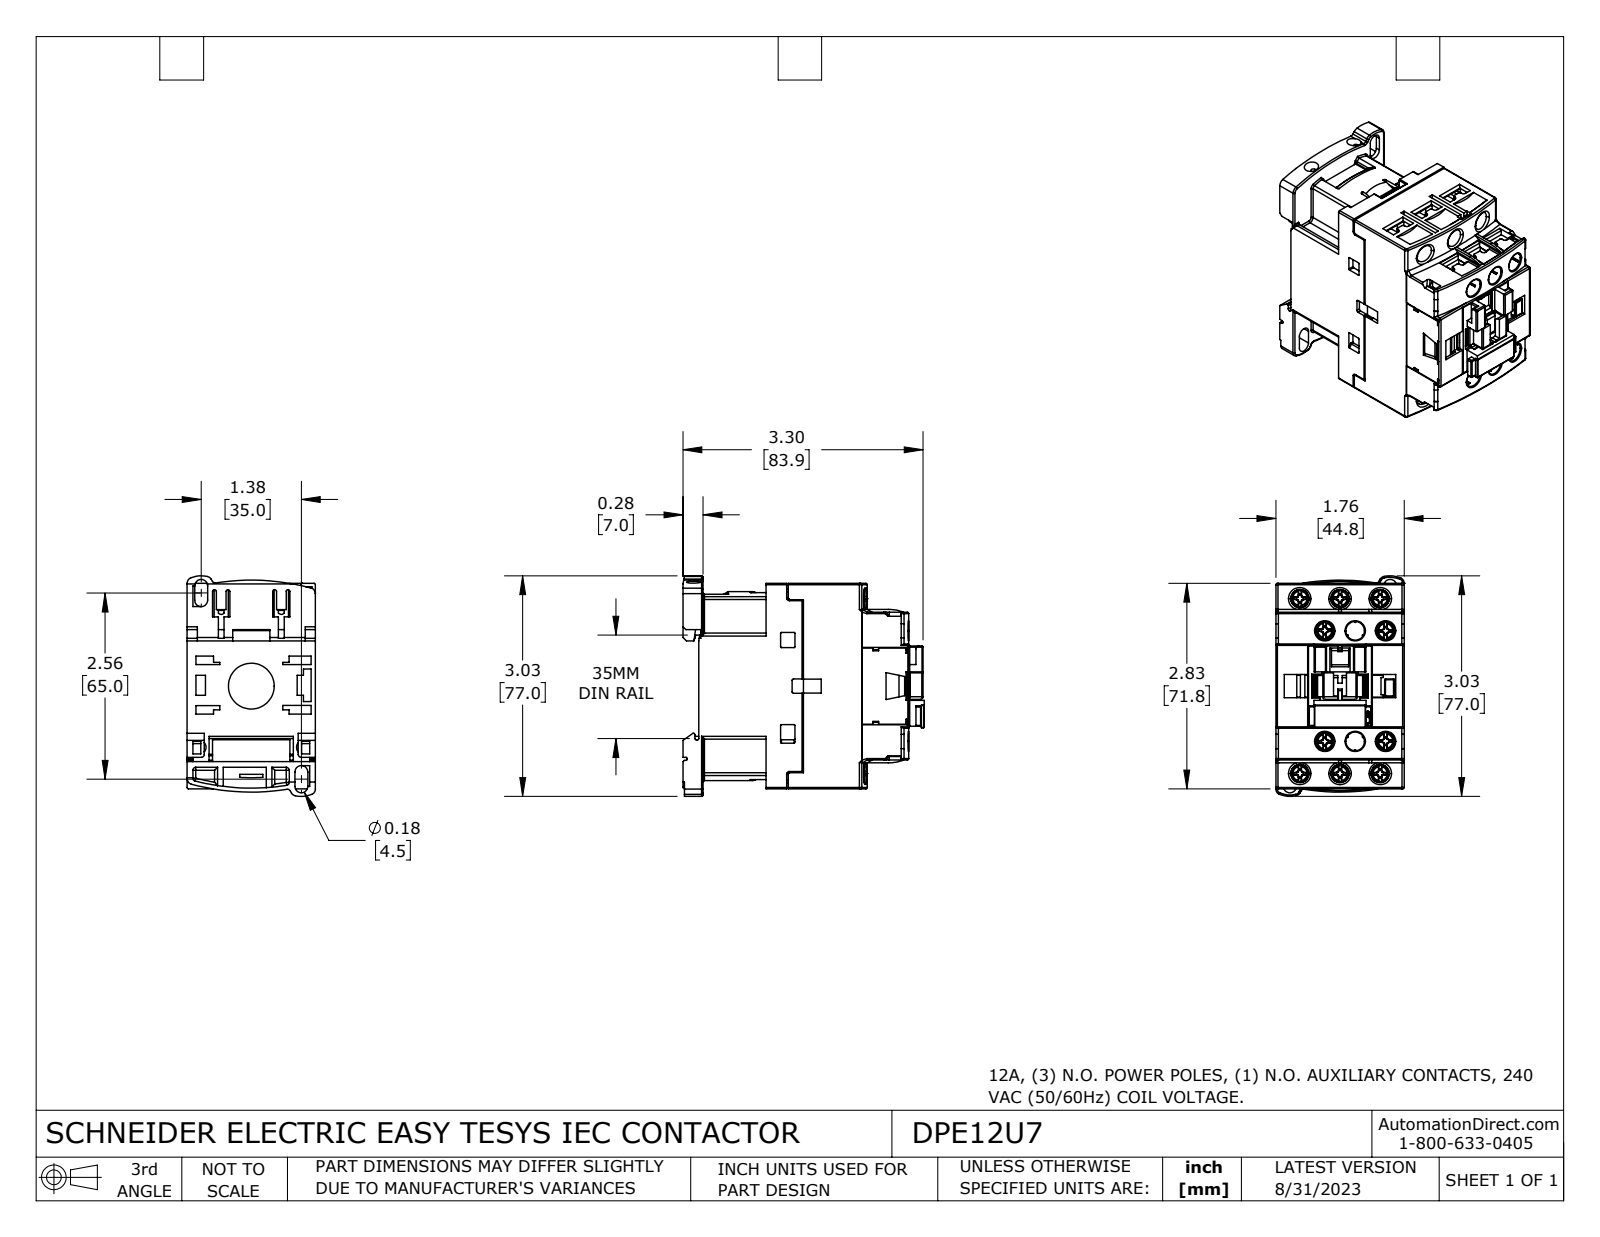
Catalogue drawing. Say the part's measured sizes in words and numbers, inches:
The part is named "DPE12U7". Its 3-D file was written by "SolidWorks 2021 (CONFIG_CONTROL_DESIGN)". It is 20 solids with 3363 faces: 2297 planar, 694 cylindrical and 372 other. Overall it measures 3.317 by 3.031 by 1.783 inches. Its volume is 8.907 cubic inches and its surface area 103.4 square inches. Round holes: 6 of diameter 0.252, 6 of diameter 0.256, 2 of diameter 0.197, 1 of diameter 0.167, 1 of diameter 0.63. Round bosses or shafts: 10 of diameter 0.138, 10 of diameter 0.108, 6 of diameter 0.315. Partial cylindrical surfaces (rounded edges, fillets, slot ends): 78 of radius 0.02, 64 of radius 0.012, 61 of radius 0.039, 42 of radius 0.006, 24 of radius 0.016, 9 of radius 0.63, 8 of radius 0.024, 7 of radius 0.079. The main face-to-face distances are 0.047, 1.764, 1.717, 0.321, 1.128, 0.807, 0.35, 2.78, 1.366, 1.118. The hole center spacings are 0.417, 0.488, 0.551, 0.558, 0.788, 0.878, 1.321, 1.576.
